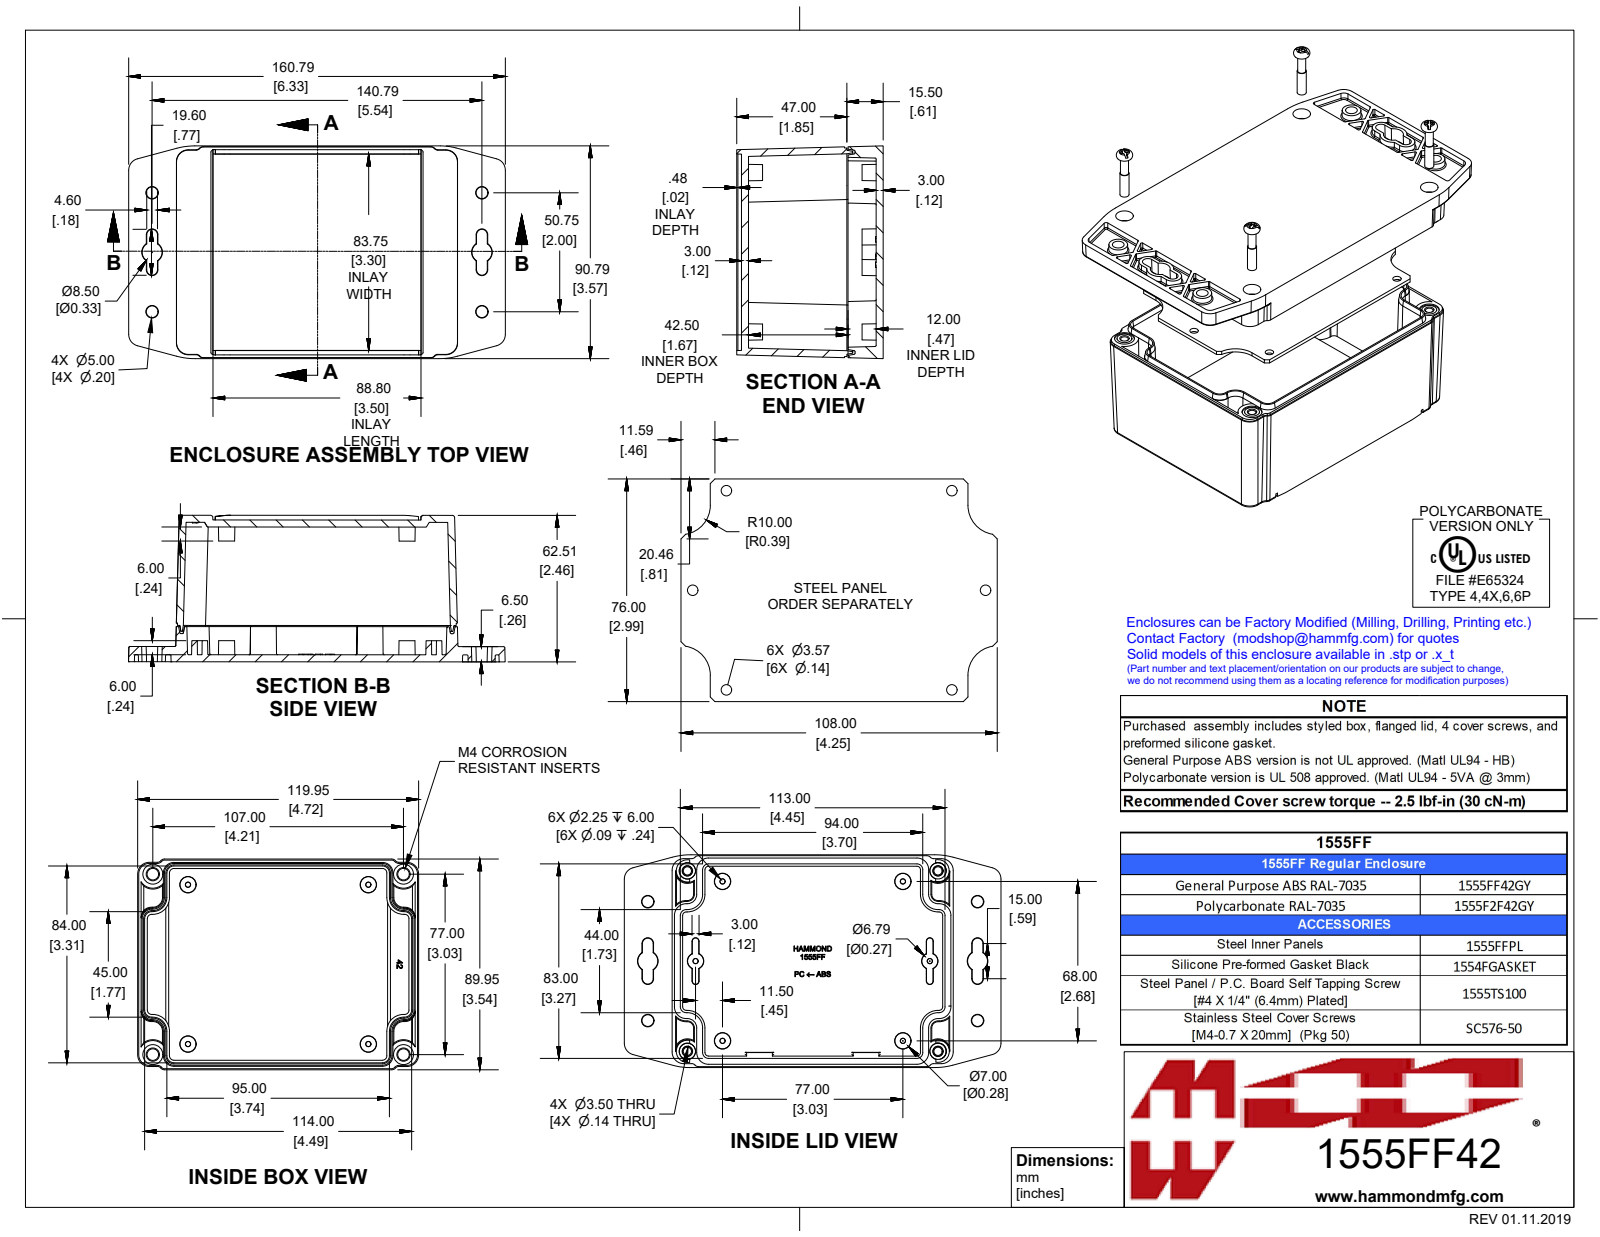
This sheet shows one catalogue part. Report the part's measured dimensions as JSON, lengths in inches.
{"part_name": "1555FF42GY", "step_written_by": "SolidWorks 2019 (CONFIG_CONTROL_DESIGN)", "units": "inches", "bodies": {"solids": 10, "faces": 1362, "planar": 629, "cylindrical": 251, "other": 482}, "overall_size": [6.33, 3.574, 2.461], "volume_in3": 10.49, "surface_area_in2": 183, "round_holes": [[0.128, 4], [0.138, 4], [0.335, 4]], "round_bosses_or_shafts": [[0.25, 4], [0.218, 4], [0.21, 4], [0.153, 4], [0.135, 4]], "partial_cylinders_radius": [[0.02, 127], [0.197, 12], [0.039, 6], [0.089, 4], [0.138, 4], [0.187, 4], [0.976, 1], [1, 1]], "face_to_face_distances": [0.118, 2.264, 2.146, 2.382, 0.059, 0.079, 2.343, 0.256, 0.138, 0.118], "hole_center_spacings": [3.031, 4.213, 5.19]}
